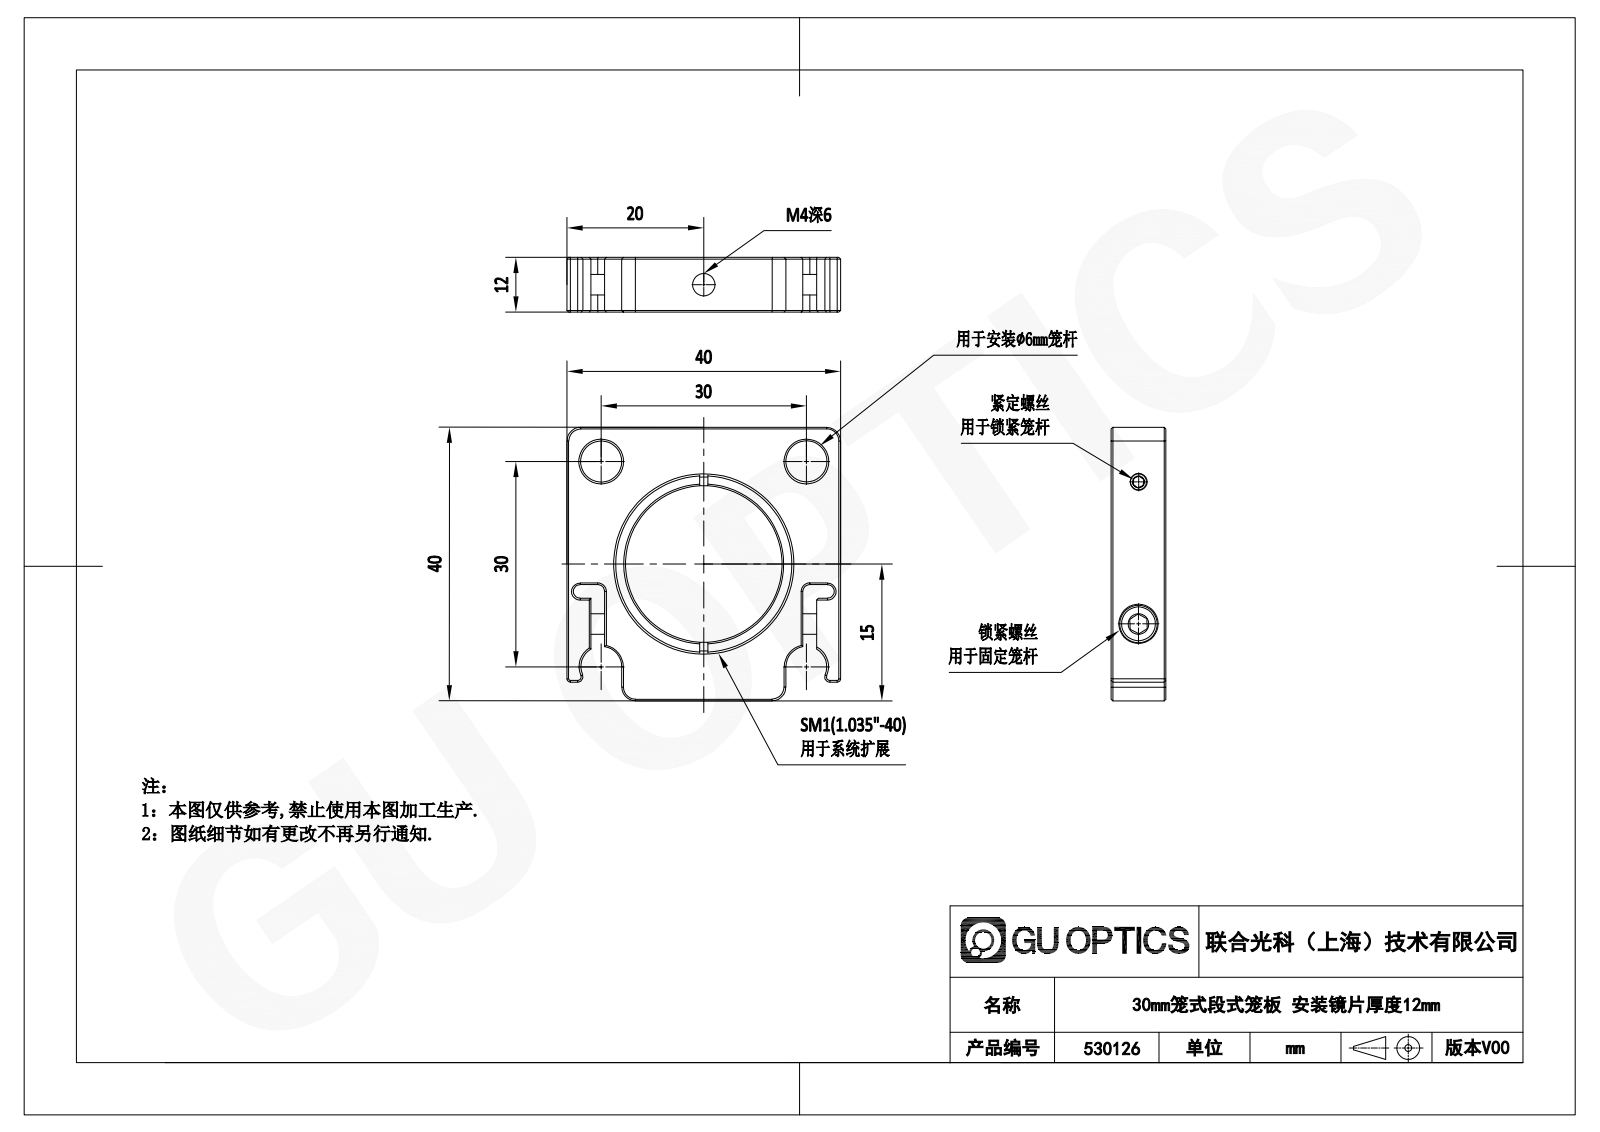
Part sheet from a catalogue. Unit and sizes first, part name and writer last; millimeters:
Units: millimetres
Overall size (bounding box): 40 × 40 × 12
Round holes (diameter × count): ⌀2.5 ×3, ⌀6 ×2, ⌀3.2 ×1, ⌀3.3 ×1, ⌀5.8 ×1, ⌀22.9 ×1, ⌀25.4 ×1
Round bosses / shafts (diameter × count): ⌀3 ×3, ⌀26.29 ×1, ⌀5.5 ×1
Partial cylindrical surfaces — rounded edges, fillets, slot ends (radius × count): R1 ×4, R2 ×4, R0.5 ×2, R0.75 ×2, R3 ×2
Main face-to-face distances: 12, 40, 2, 5.5, 34.5, 10, 8, 3.5, 36.5, 31
Hole centre spacings: 20.97, 21.21, 6, 30
Volume: 10 967 mm³ · Surface area: 7 540 mm²
Bodies: 10 solids, 284 faces (138 planar, 43 cylindrical, 103 other)
Part name (STEP PRODUCT): 530126
STEP written by: SolidWorks 2020 (CONFIG_CONTROL_DESIGN)
